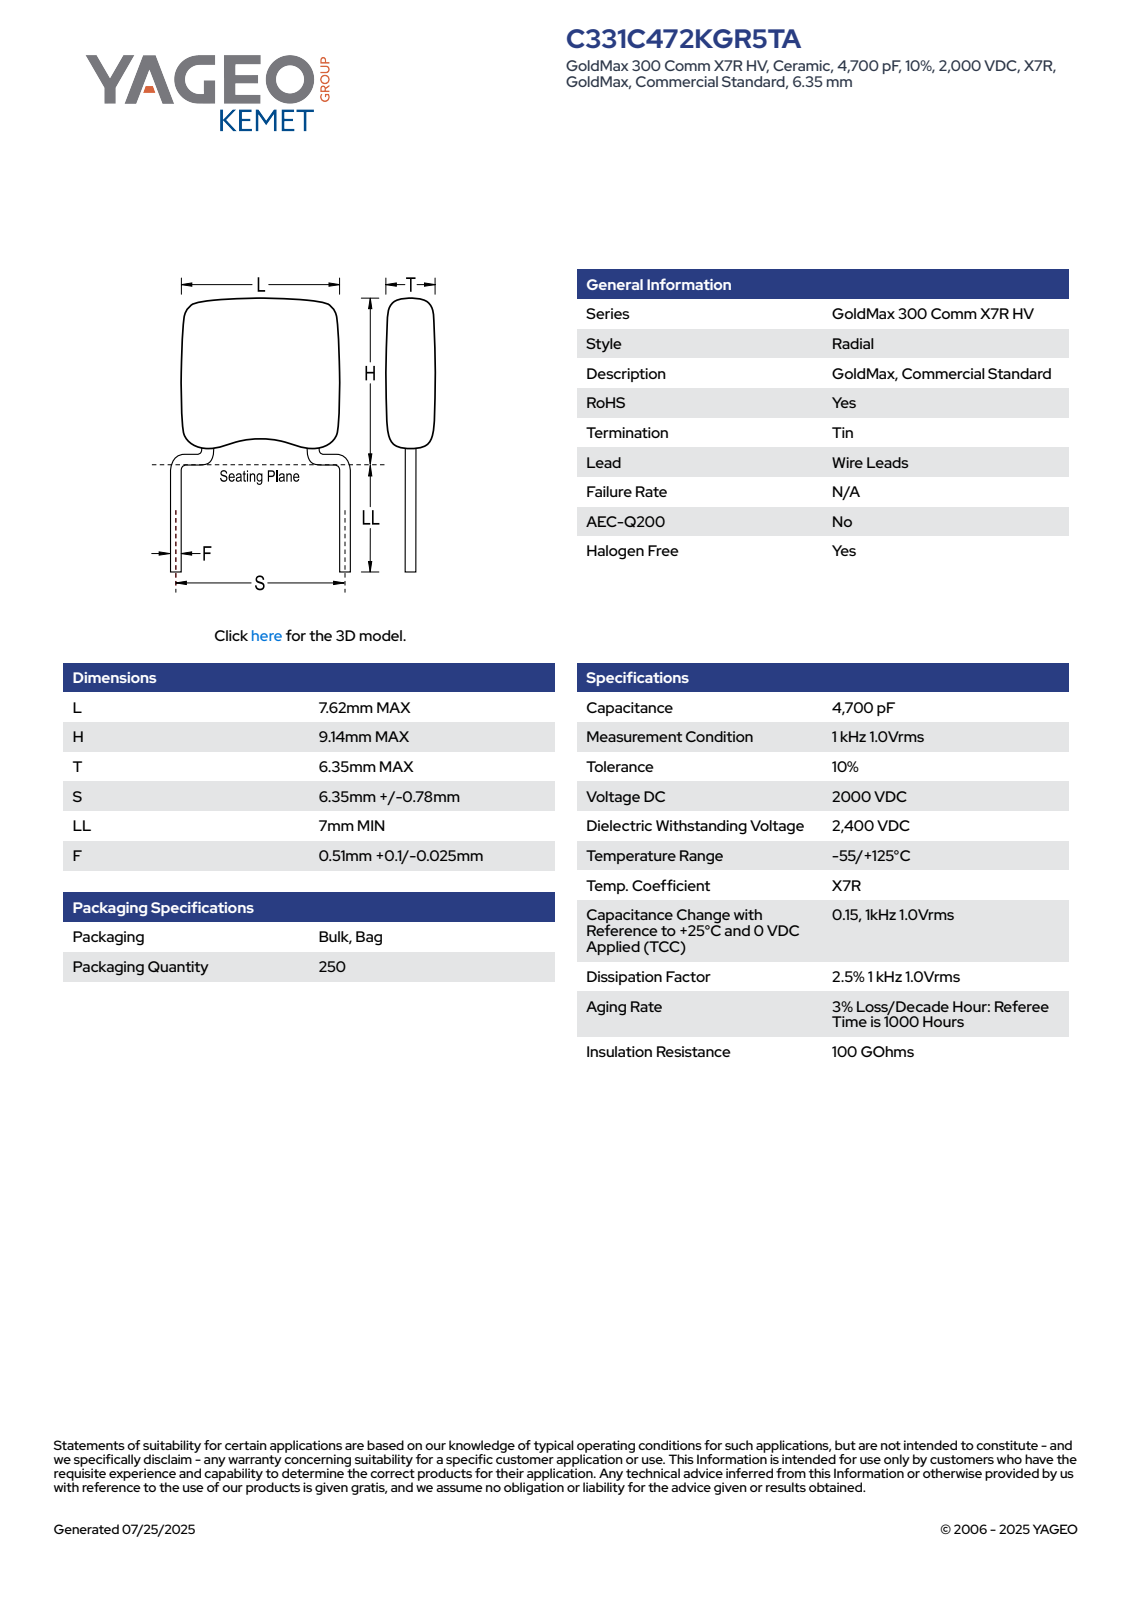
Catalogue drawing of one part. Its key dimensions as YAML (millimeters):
part_name: "CCR_SB_7.62X9.14_L7.62H9.14T6.35S6.35LL7F0.51"
step_written_by: "SolidWorks 2014 (AUTOMOTIVE_DESIGN)"
units: millimeters
bodies: {solids: 4, faces: 97, planar: 65, cylindrical: 14, other: 18}
overall_size: [16.14, 7.62, 6.36]
volume: 339
surface_area: 299
round_bosses_or_shafts:
  - {diameter: 0.51, count: 2}
partial_cylinders:
  - {radius: 1, count: 10}
face_to_face_distances: [6.35, 7.62, 7.22, 0.65, 3.96, 3.26, 3.31, 3.91, 0.4, 1.33]
